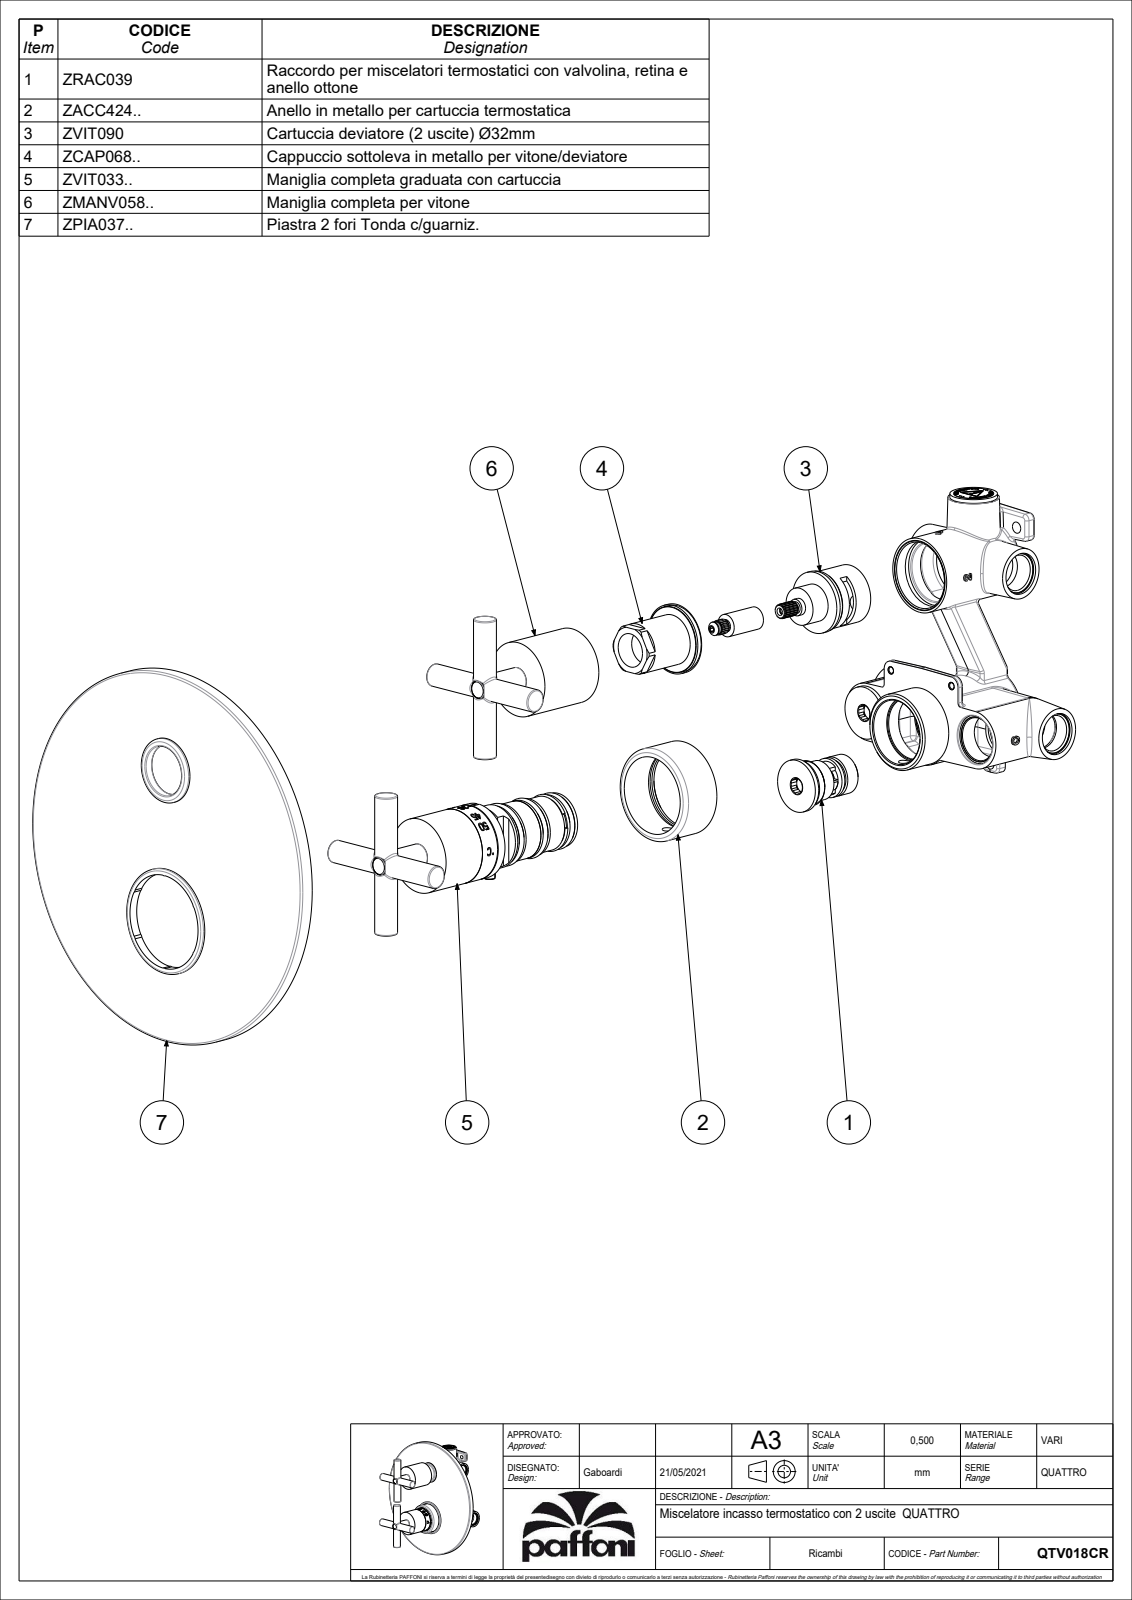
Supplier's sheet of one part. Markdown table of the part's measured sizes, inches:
| quantity | value |
| --- | --- |
| part name | QTV018CR |
| STEP written by | CREO PARAMETRIC BY PTC INC, 2020044 (CONFIG_CONTROL_DESIGN) |
| units | inches |
| bodies | 5 solids, 1690 faces (1097 planar, 295 cylindrical, 298 other) |
| overall size | 7.874 × 7.874 × 3.743 |
| volume | 15.82 in³ |
| surface area | 236.2 in² |
| round holes (diameter × count) | 0.177 × 2, 0.276 × 2, 0.315 × 2, 1.417 × 2, 0.118 × 1, 0.13 × 1, 0.138 × 1, 0.157 × 1, 0.256 × 1, 0.335 × 1, 0.709 × 1, 0.787 × 1 |
| round bosses / shafts (diameter × count) | 0.472 × 5, 1.575 × 2, 1.358 × 2, 1.055 × 2, 0.551 × 2, 0.512 × 2, 0.354 × 2, 7.874 × 1 |
| partial cylindrical surfaces (radius × count) | 0.02 × 28, 0.062 × 6, 0.118 × 4, 0.012 × 2, 0.187 × 2, 0.039 × 1, 0.057 × 1, 0.138 × 1 |
| main face-to-face distances | 0.315, 0.276, 0.039, 0.472, 0.118, 2.071, 2.465, 2.522, 2.189, 2.246 |
| hole center spacings | 0.197, 1.35, 1.365, 1.878, 3.228, 3.234 |
